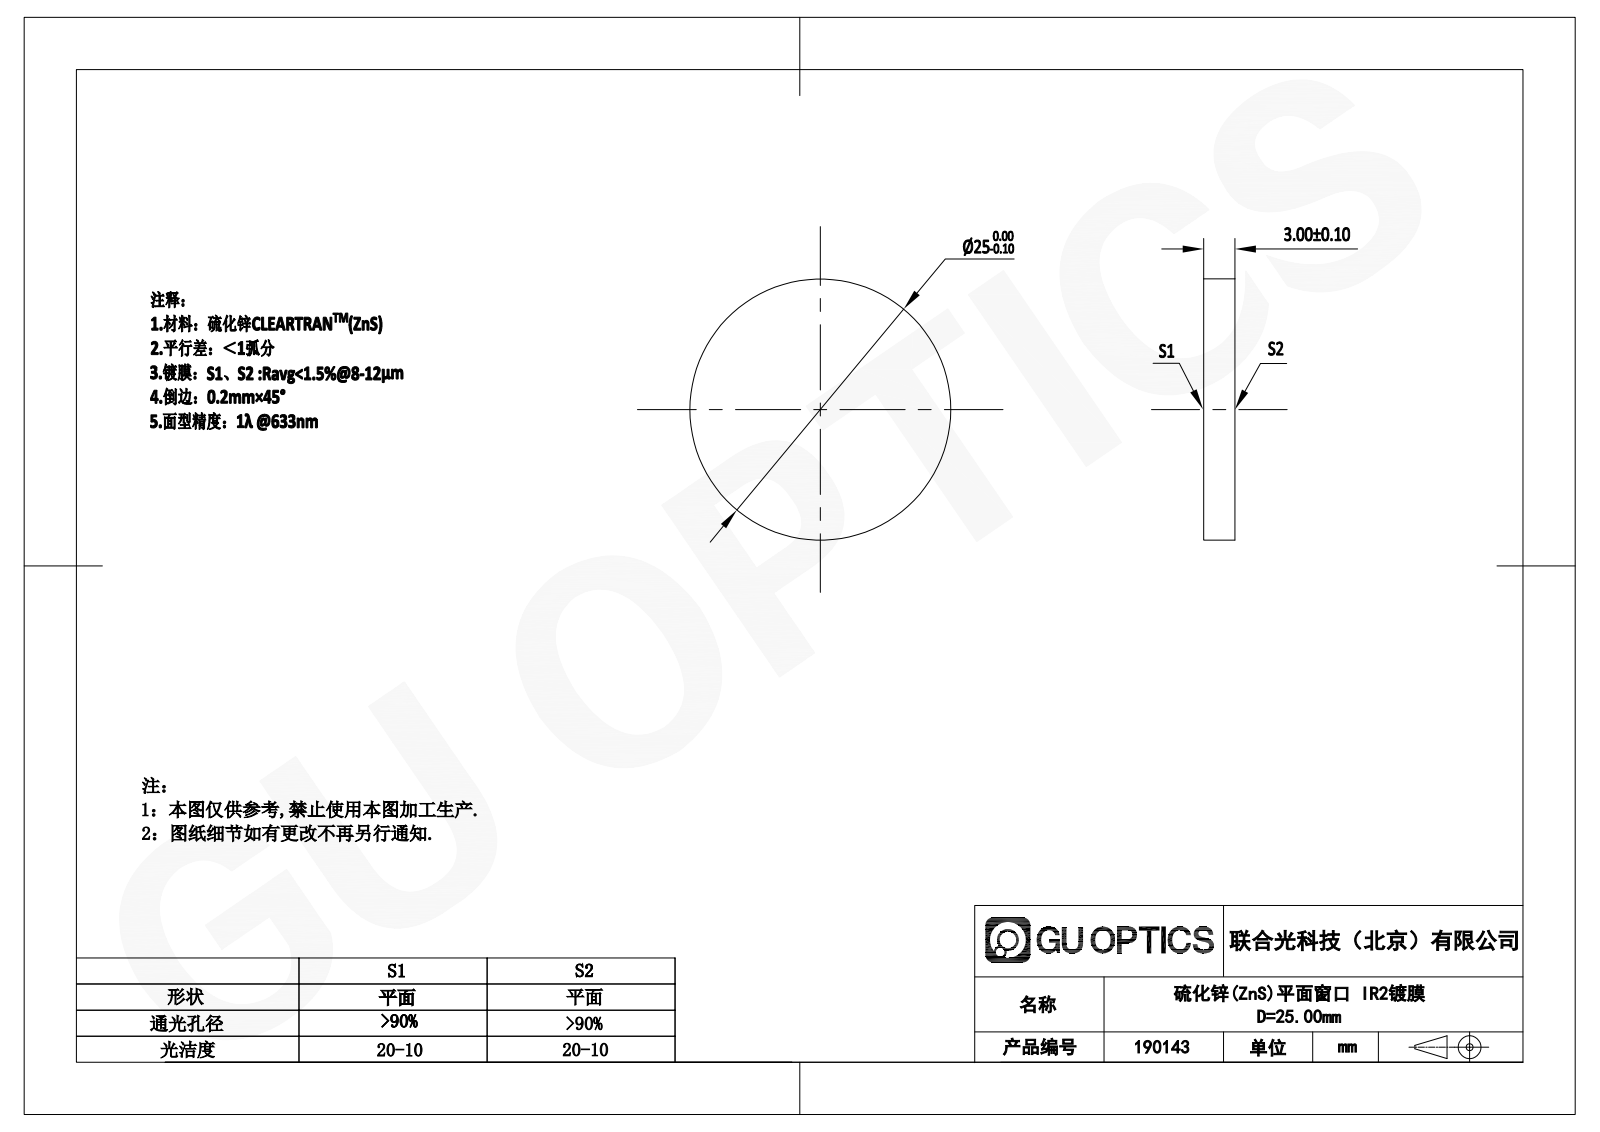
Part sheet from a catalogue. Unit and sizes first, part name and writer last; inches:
Units: inches
Overall size (bounding box): 0.984 × 0.984 × 0.118
Round bosses / shafts (diameter × count): ⌀0.984 ×1
Main face-to-face distances: 0.118
Volume: 0.09 in³ · Surface area: 1.886 in²
Bodies: 1 solid, 4 faces (2 planar, 2 cylindrical, 0 other)
Part name (STEP PRODUCT): 190142
STEP written by: SolidWorks 2016 (AUTOMOTIVE_DESIGN)
